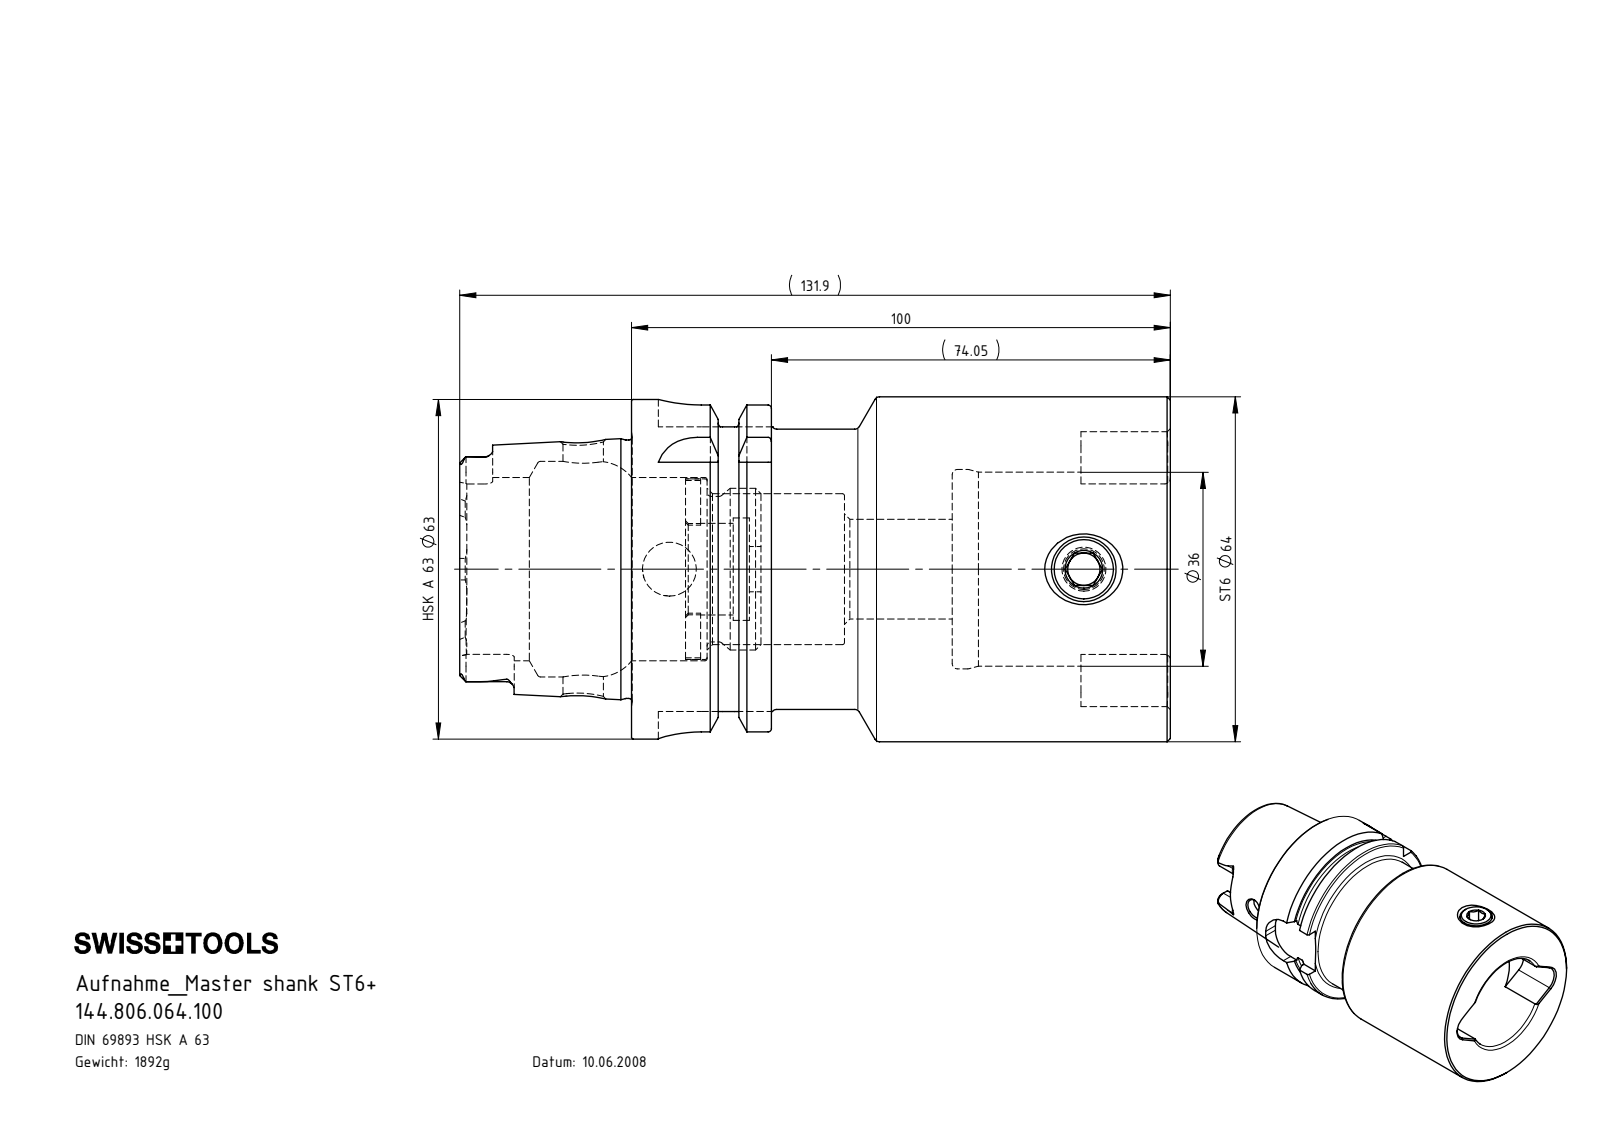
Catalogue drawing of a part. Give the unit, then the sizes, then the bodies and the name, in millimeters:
Units: millimetres
Overall size (bounding box): 131.9 × 64 × 64
Round holes (diameter × count): ⌀6 ×1, ⌀7.5 ×1, ⌀8.4 ×1, ⌀10 ×1, ⌀11 ×1, ⌀17 ×1, ⌀18.5 ×1, ⌀19 ×1, ⌀28 ×1, ⌀34 ×1, ⌀36 ×1, ⌀37 ×1
Round bosses / shafts (diameter × count): ⌀64 ×1, ⌀63 ×1, ⌀54.95 ×1, ⌀52 ×1, ⌀47.94 ×1, ⌀33.5 ×1, ⌀30 ×1, ⌀27 ×1
Partial cylindrical surfaces — rounded edges, fillets, slot ends (radius × count): R1.4 ×6, R2.88 ×4, R8 ×4, R5.2 ×2
Main face-to-face distances: 100, 10, 14, 59.5, 40.5, 24, 49.5, 90, 25.95, 15.95
Hole centre spacings: 76.95
Volume: 241 056 mm³ · Surface area: 50 490 mm²
Bodies: 3 solids, 269 faces (81 planar, 70 cylindrical, 118 other)
Part name (STEP PRODUCT): ST6-ER4.002.014_A; HA6-ST6.K01.100_B_Fertigbearbeitung; ST6-ER1.001.018_A; 144.806.064.100
STEP written by: SolidWorks 2017 (CONFIG_CONTROL_DESIGN)
